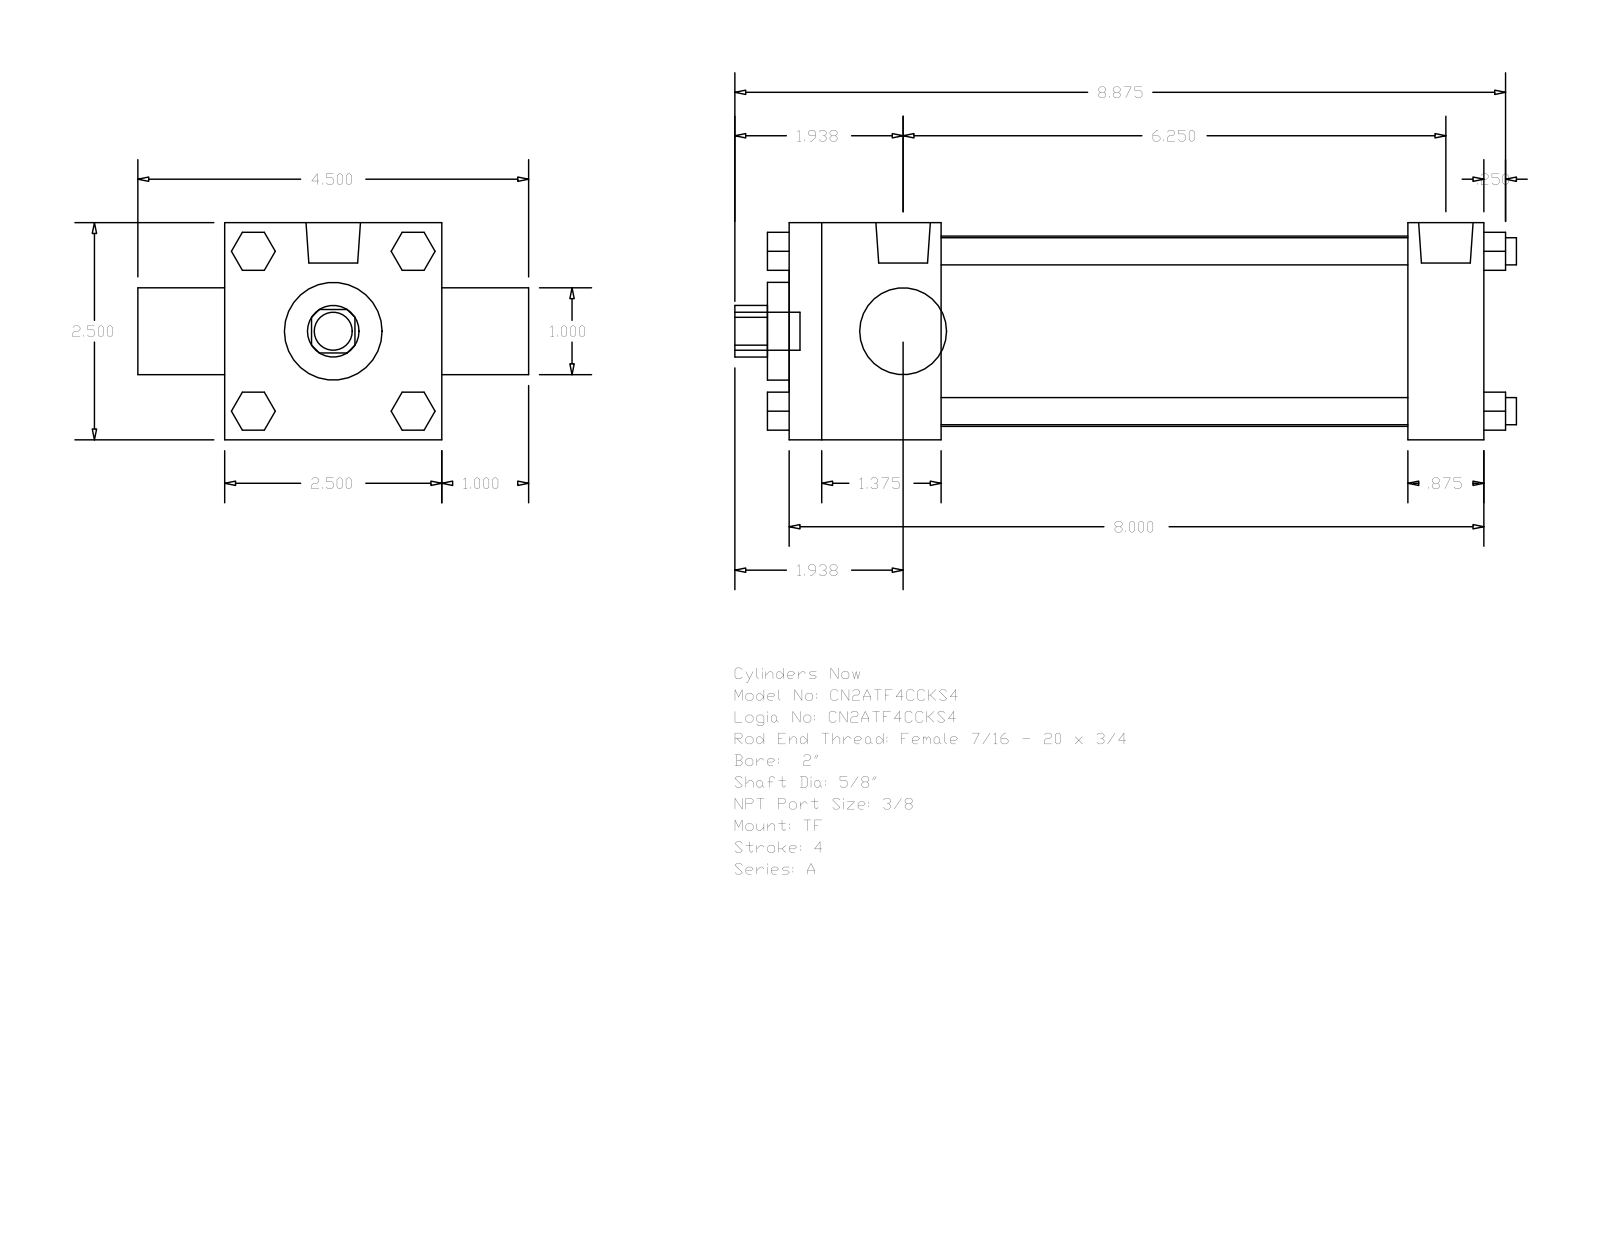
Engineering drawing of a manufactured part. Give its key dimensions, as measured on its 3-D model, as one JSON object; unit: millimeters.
{"part_name": "A_TF__0200_0.625", "step_written_by": "GSSL Pune (CONFIG_CONTROL_DESIGN)", "units": "millimeters", "bodies": {"solids": 0, "faces": 120, "planar": 92, "cylindrical": 28, "other": 0}, "overall_size": [228.6, 114.3, 63.5], "round_holes": [[15.88, 1], [25.4, 1], [28.57, 1], [55.63, 1]], "round_bosses_or_shafts": [[7.94, 4], [5.56, 3], [15.93, 2], [11.11, 1]], "partial_cylinders_radius": [[7.54, 1]], "face_to_face_distances": [63.5, 203.19, 44.45, 180.97, 136.52, 158.74, 22.22, 25.4, 88.9, 50.8]}
